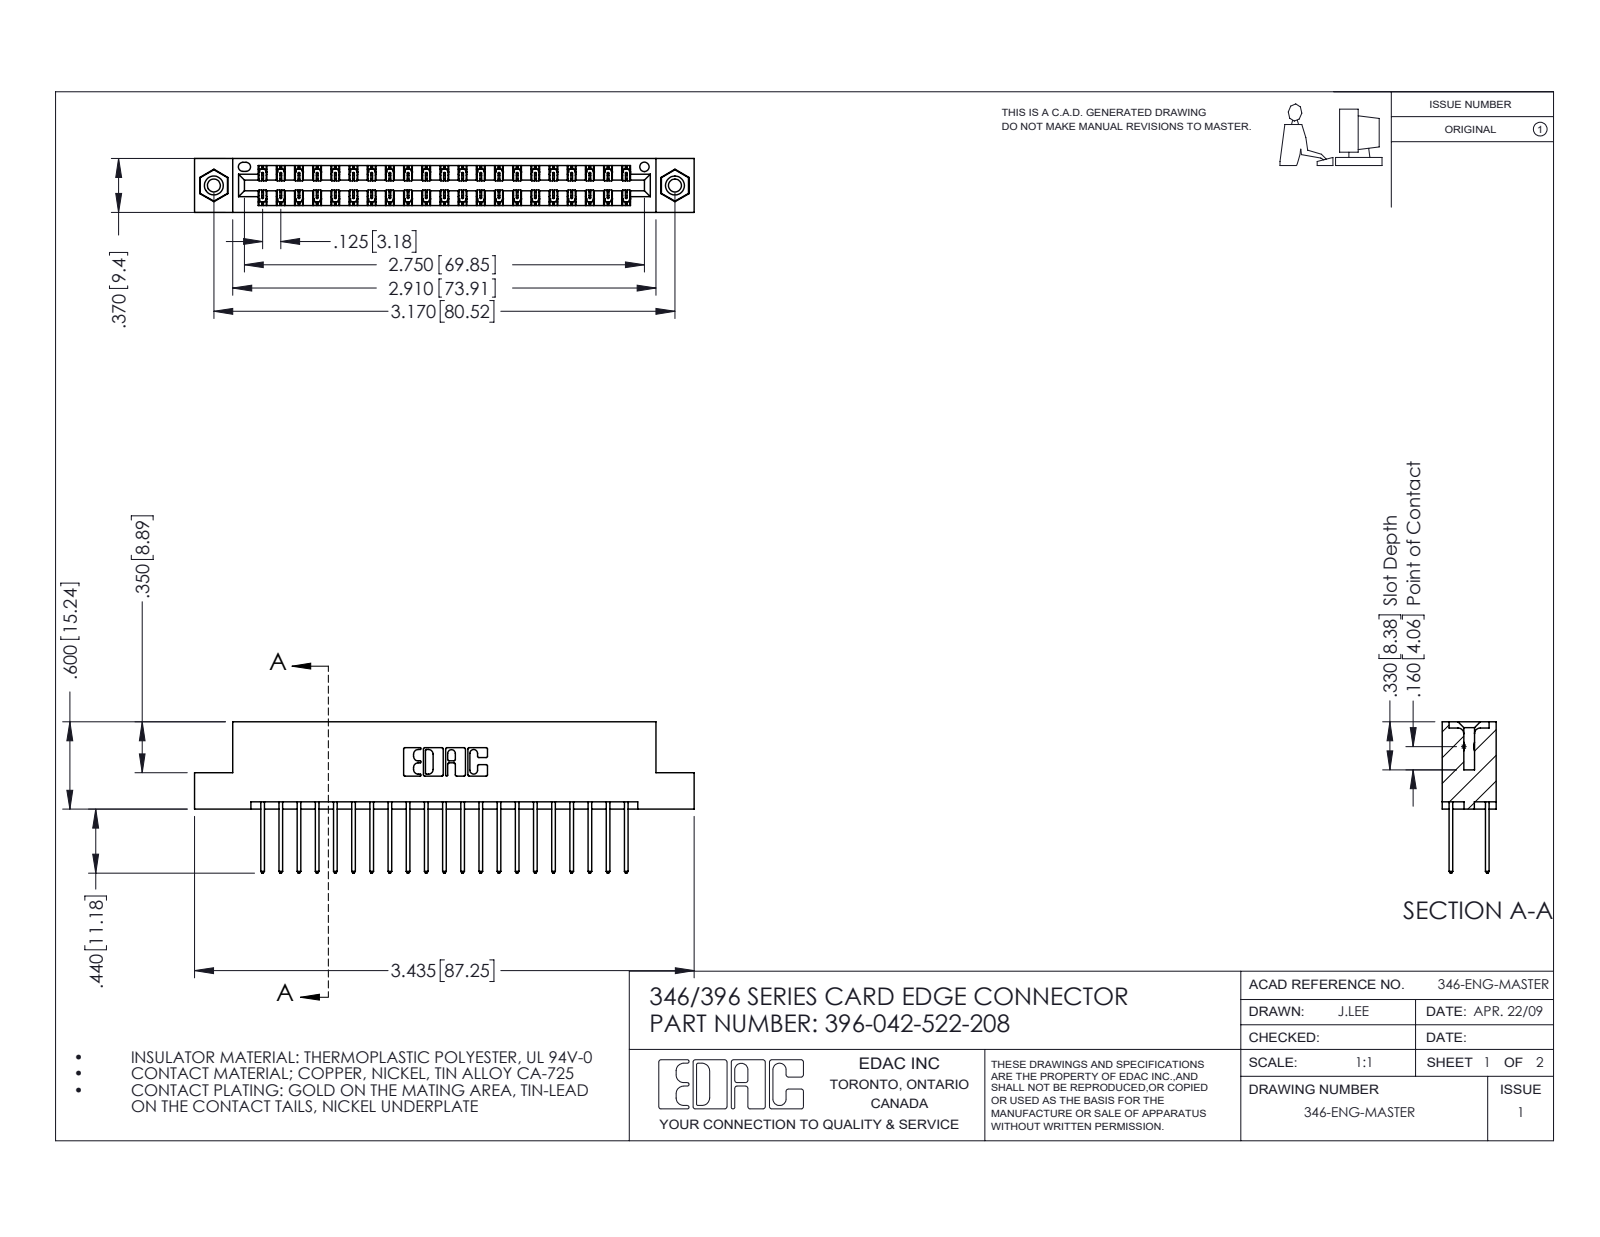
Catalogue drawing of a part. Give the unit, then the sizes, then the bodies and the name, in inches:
Units: inches
Overall size (bounding box): 3.435 × 1.04 × 0.37
Round holes (diameter × count): ⌀0.089 ×2, ⌀0.125 ×2, ⌀0.156 ×2, ⌀0.064 ×1
Round bosses / shafts (diameter × count): ⌀0.155 ×2
Partial cylindrical surfaces — rounded edges, fillets, slot ends (radius × count): R0.006 ×63, R0.01 ×42, R0.01 ×22, R0.007 ×6, R0.031 ×6, R0.026 ×3, R0.014 ×2, R0.022 ×2
Main face-to-face distances: 0.048, 0.322, 0.25, 0.37, 0.072, 0.298, 0.025, 0.275, 0.148, 0.222
Hole centre spacings: 0.246, 2.963, 3.17
Volume: 0.515 in³ · Surface area: 18.29 in²
Bodies: 45 solids, 2366 faces (1578 planar, 772 cylindrical, 16 other)
Part name (STEP PRODUCT): 345-292-001_345-293-122; 396-042-522-208; 345-250-001_345-250-003-102; 346 Part_Flush Mounting Lugs - 0.156 Dia-TI
STEP written by: SolidWorks 2016 (CONFIG_CONTROL_DESIGN)
